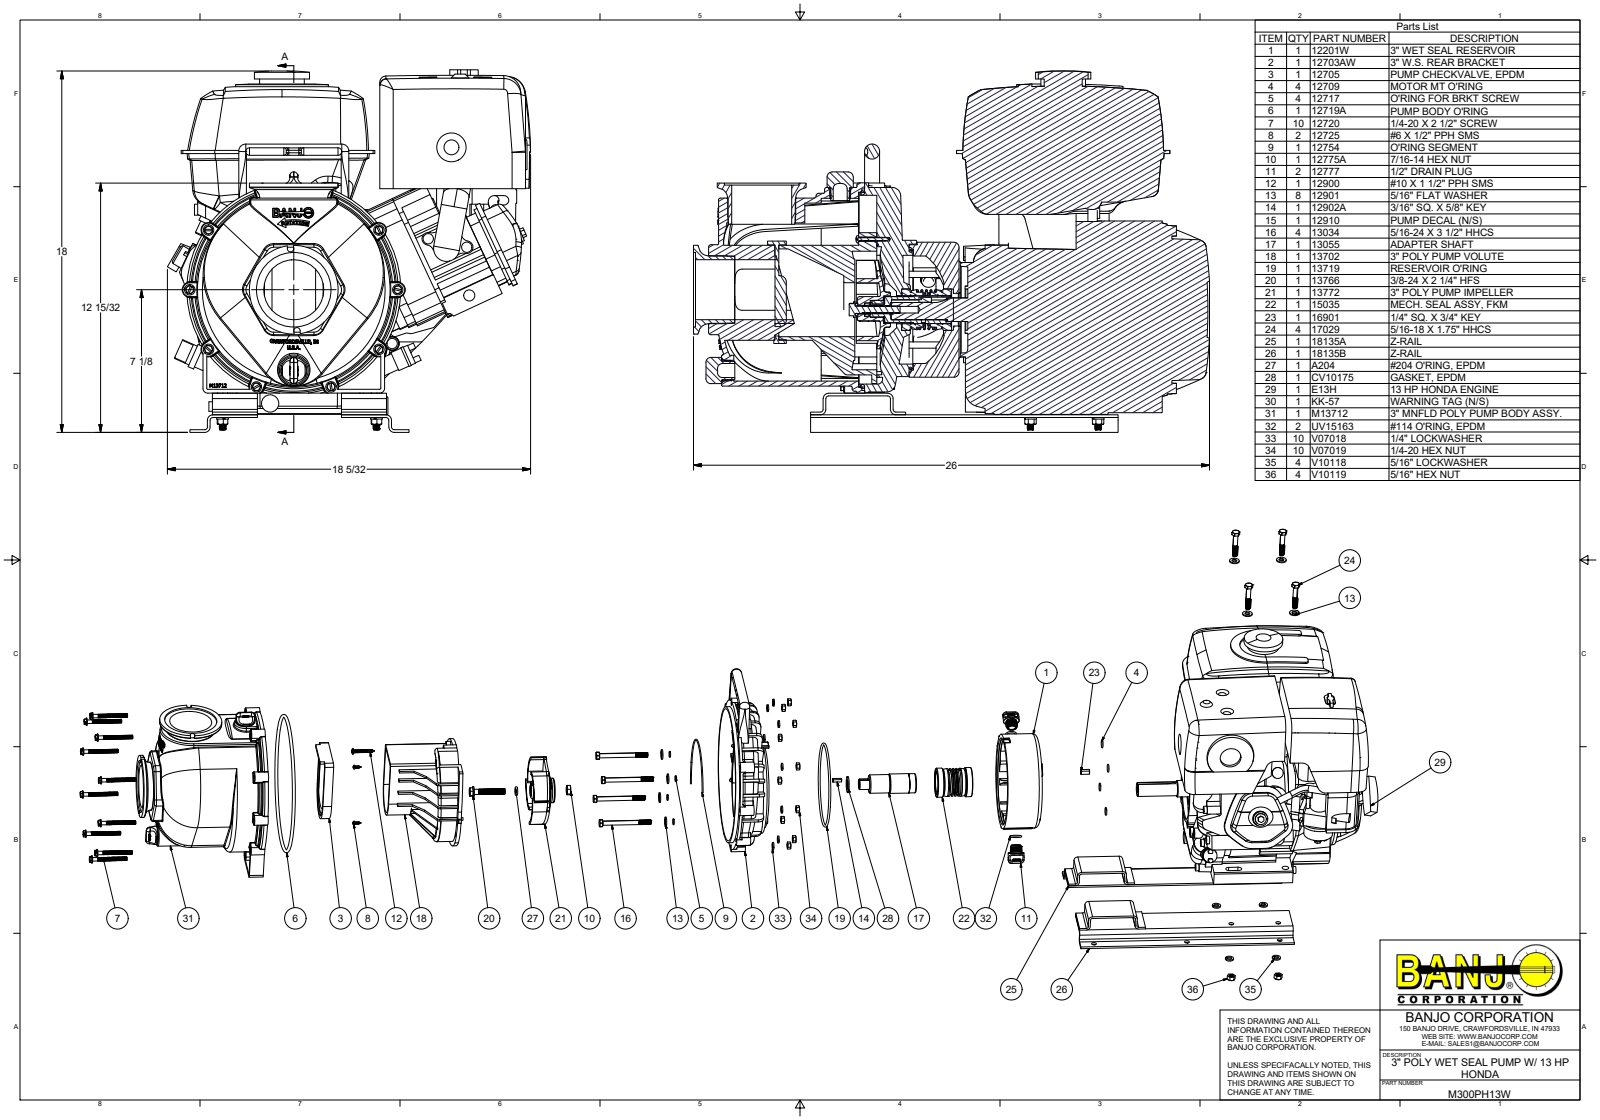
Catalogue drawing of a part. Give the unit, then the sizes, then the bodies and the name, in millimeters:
Units: millimetres
Overall size (bounding box): 673.31 × 461.24 × 460.52
Round holes (diameter × count): ⌀8.73 ×16, ⌀4.98 ×10, ⌀6.4 ×10, ⌀6.86 ×10, ⌀11.91 ×8, ⌀14.25 ×8, ⌀5.59 ×7, ⌀8 ×6, ⌀6.41 ×4, ⌀7.95 ×4, ⌀8.18 ×4, ⌀2.87 ×2
Round bosses / shafts (diameter × count): ⌀7.02 ×80, ⌀6.82 ×60, ⌀13 ×17, ⌀13.21 ×10, ⌀12.42 ×10, ⌀6.35 ×10, ⌀17.48 ×8, ⌀9.68 ×8
Partial cylindrical surfaces — rounded edges, fillets, slot ends (radius × count): R0.76 ×140, R3.17 ×81, R0.38 ×61, R1.52 ×51, R20 ×43, R4.76 ×35, R10 ×35, R6.35 ×27
Main face-to-face distances: 3.42, 0.5, 3.92, 290.66, 287.24, 286.74, 3.41, 27.43, 6.35, 295.62
Hole centre spacings: 78.4, 132.08, 195.5, 17.52, 45.98, 63.5, 65.02, 89.8
Volume: 37 630 000 mm³ · Surface area: 2 816 000 mm²
Bodies: 116 solids, 11185 faces (2949 planar, 3239 cylindrical, 4997 other)
Part name (STEP PRODUCT): M300PH13W; 12703AW; 12703AWX; 12703AWV (+8 more)
STEP written by: Autodesk Inventor 2017 (AUTOMOTIVE_DESIGN)
